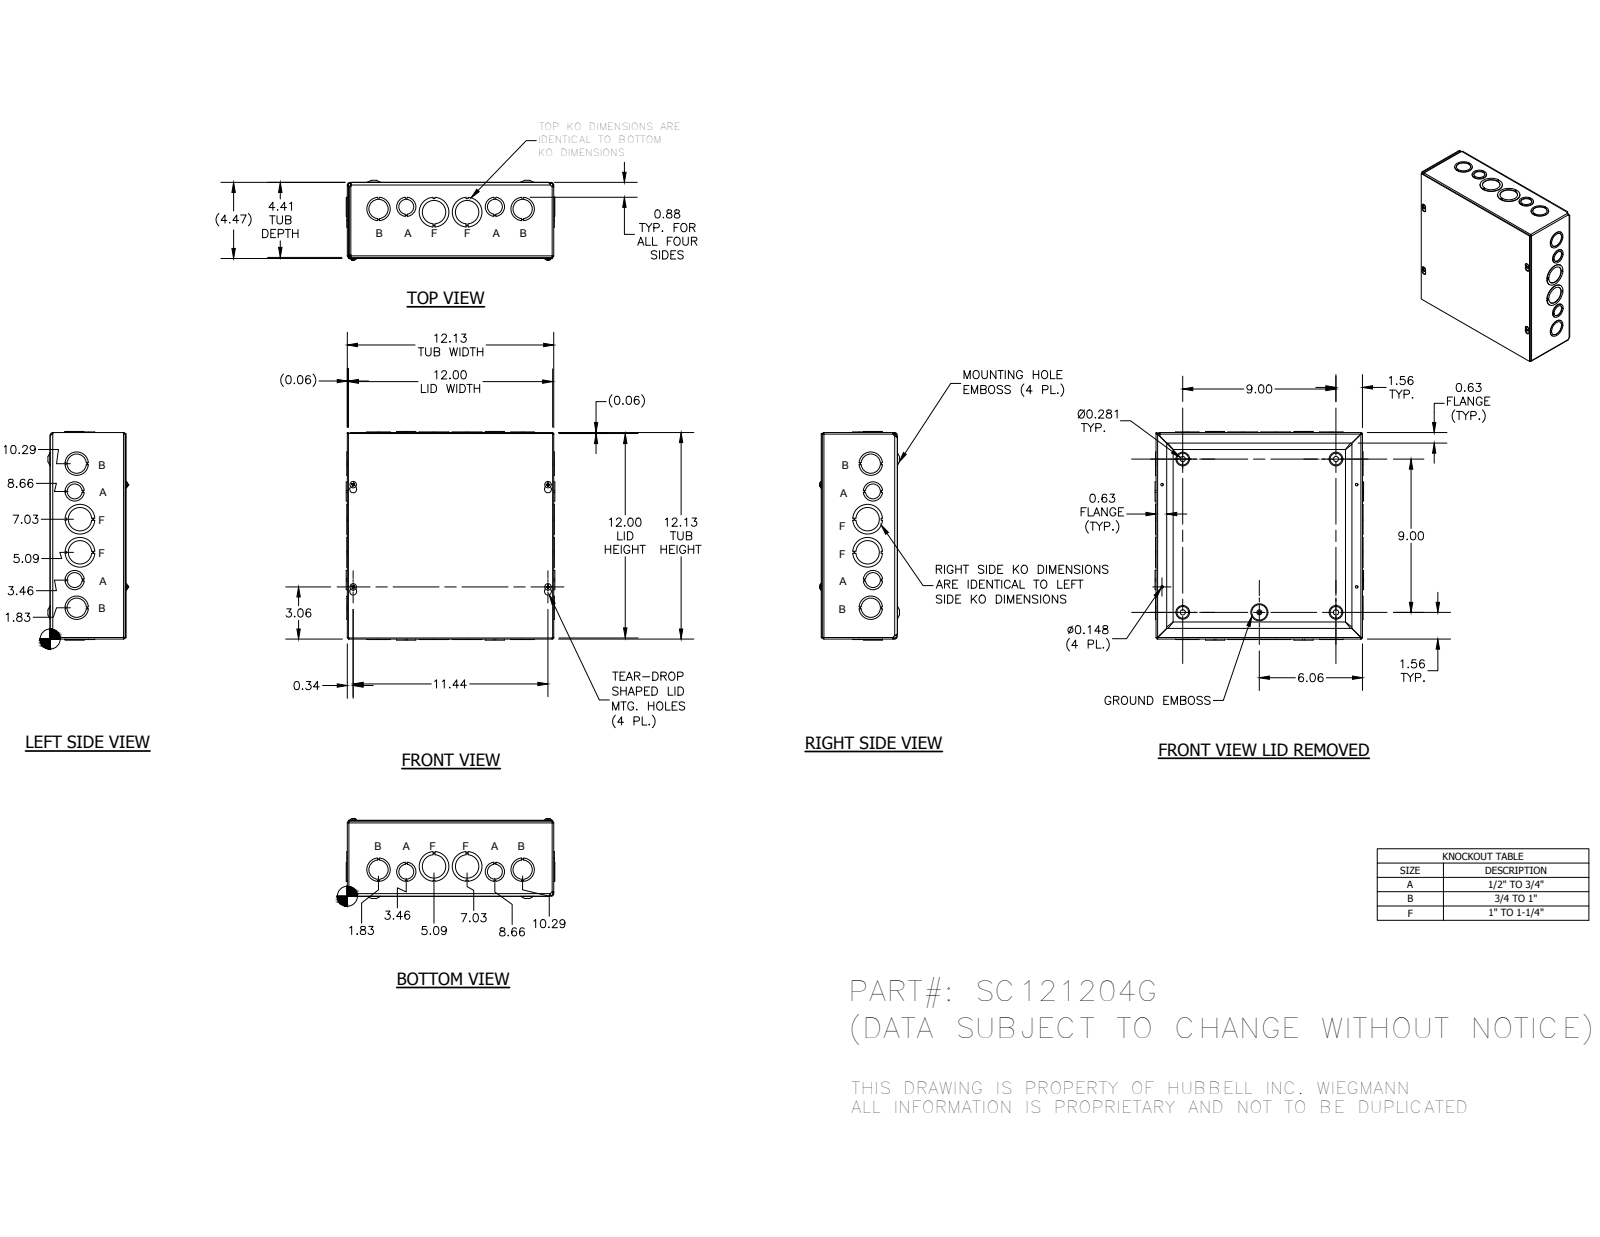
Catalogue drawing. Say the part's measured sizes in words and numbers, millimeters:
The part is named "SC1212GBKP; SC121204GWRA; SC1212GLID; 34056 (+1 more)". Its 3-D file was written by "Autodesk Inventor 2014 (AUTOMOTIVE_DESIGN)". It is 22 solids with 1030 faces: 662 planar, 217 cylindrical and 151 other. Overall it measures 311.12 by 311.12 by 119.2 millimeters. Round holes: 8 of diameter 28.57, 8 of diameter 34.92, 4 of diameter 3.76, 4 of diameter 7.62, 4 of diameter 22.22, 4 of diameter 44.45, 1 of diameter 4.19. Round bosses or shafts: 4 of diameter 9.75, 4 of diameter 4.17, 1 of diameter 5.8. Partial cylindrical surfaces (rounded edges, fillets, slot ends): 8 of radius 0.79, 8 of radius 2.37, 4 of radius 1.4, 4 of radius 1.57, 4 of radius 2.38, 4 of radius 2.79, 4 of radius 2.97, 4 of radius 3.15. The main face-to-face distances are 1.57, 110.32, 111.89, 1.59, 111.91, 113.48, 1.58, 307.98, 306.4, 306.41. The hole center spacings are 41.52, 42.15, 49.09, 82.94, 91.03, 132.17, 173.51, 193.
